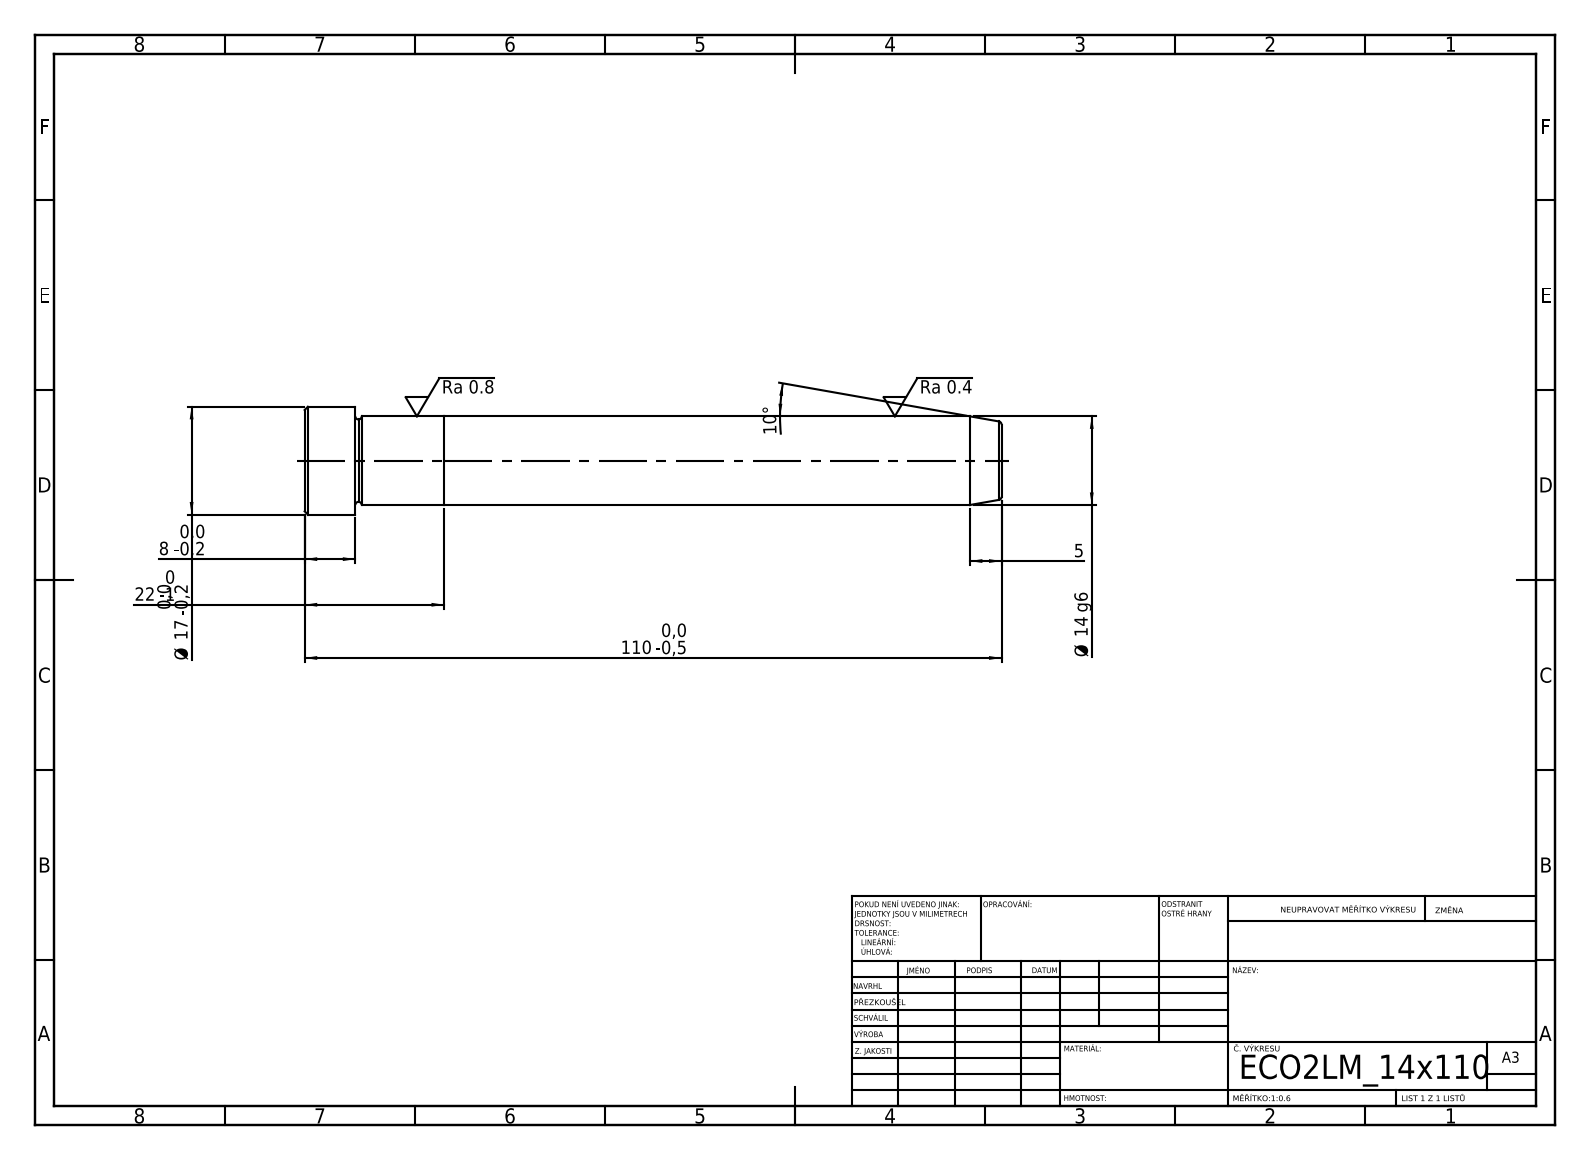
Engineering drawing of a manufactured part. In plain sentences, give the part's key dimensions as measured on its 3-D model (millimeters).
Its 3-D file was written by "SolidWorks 2019 (CONFIG_CONTROL_DESIGN)". It is 2 solids with 21 faces: 5 planar, 6 cylindrical and 10 other. Overall it measures 110 by 17 by 17 millimeters. Its volume is 17 400 cubic millimeters and its surface area 5 629 square millimeters. Round bosses or shafts: 1 of diameter 17, 1 of diameter 14. The main face-to-face distances are 22, 88, 110, 102, 14, 8.
